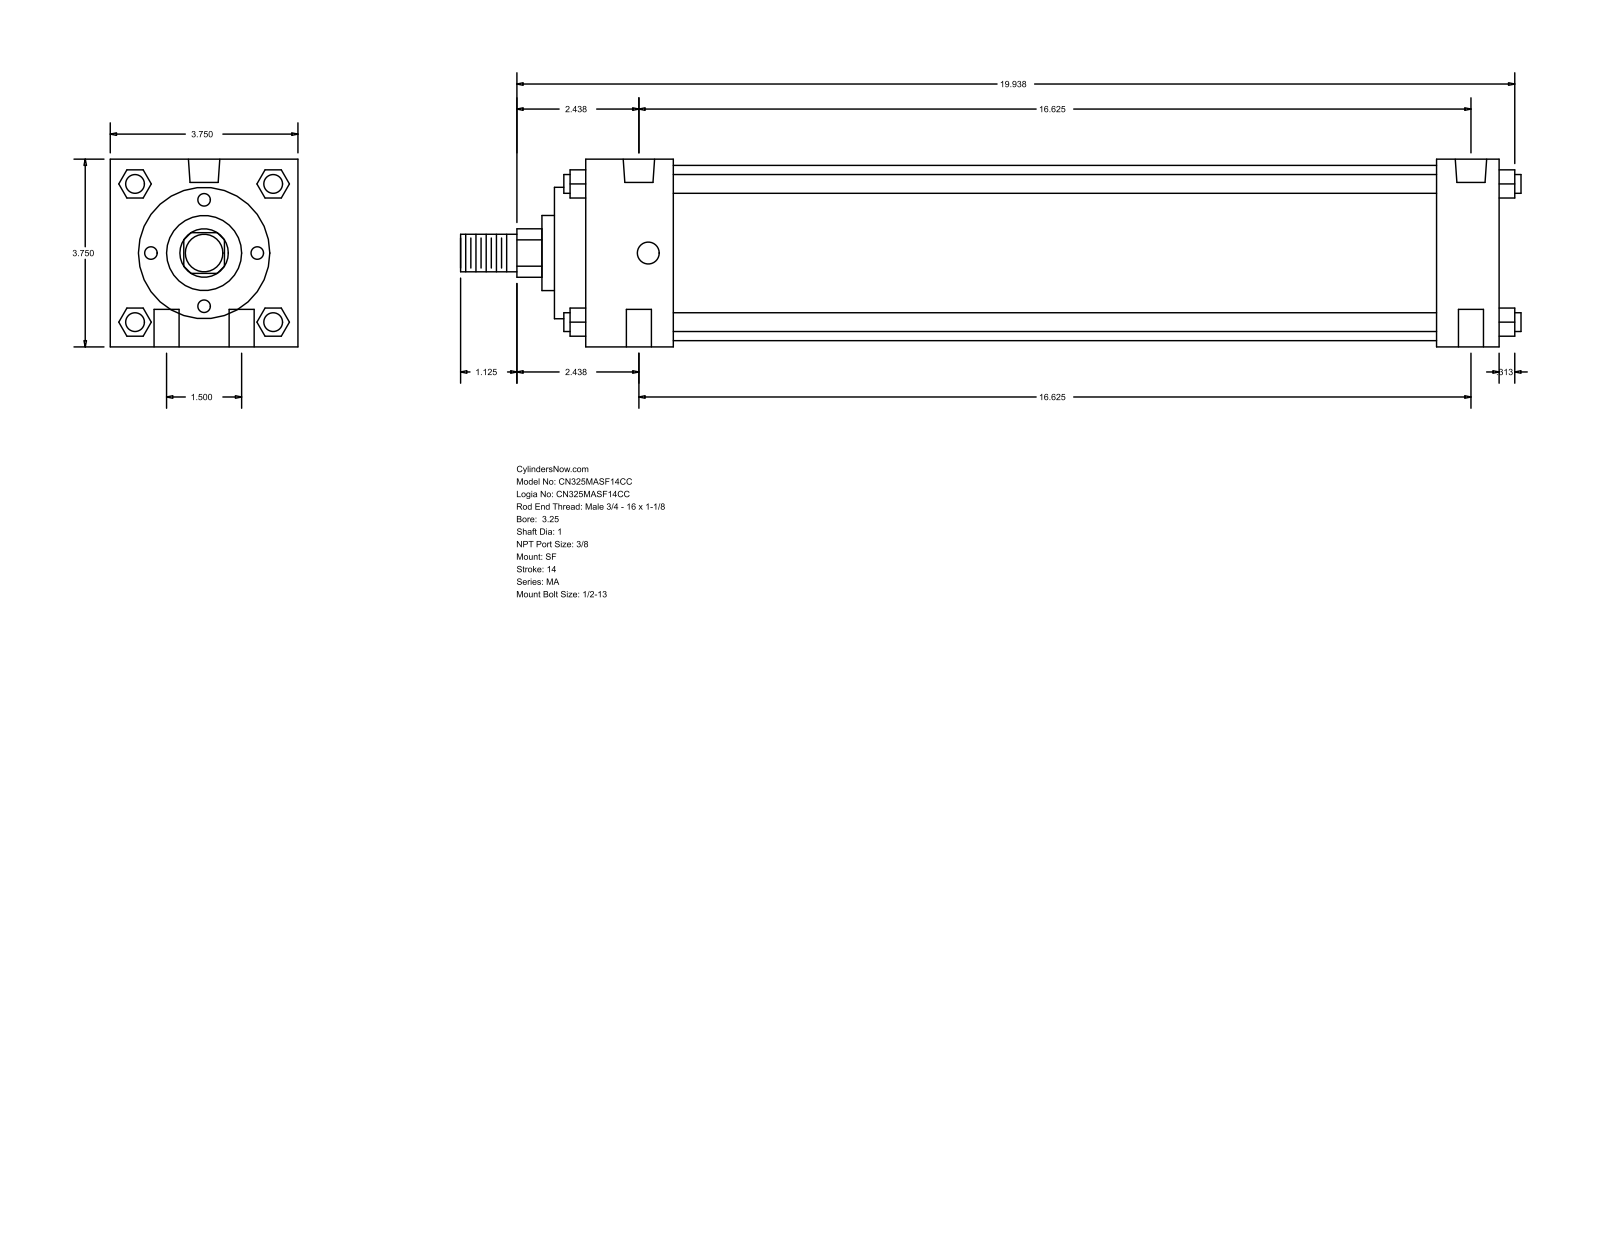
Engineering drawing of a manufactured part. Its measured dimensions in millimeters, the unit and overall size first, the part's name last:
Units: millimetres
Overall size (bounding box): 538.16 × 95.25 × 95.25
Round holes (diameter × count): ⌀12.7 ×4, ⌀11.11 ×2, ⌀15.93 ×2
Round bosses / shafts (diameter × count): ⌀9.53 ×4, ⌀88.9 ×1, ⌀66.67 ×1, ⌀38.1 ×1, ⌀25.4 ×1, ⌀19.05 ×1
Partial cylindrical surfaces — rounded edges, fillets, slot ends (radius × count): R12.29 ×1
Main face-to-face distances: 95.24, 463.56, 431.81, 31.75, 44.46, 387.35, 419.1, 15.87, 60.33, 447.68
Hole centre spacings: 19.05, 422.71, 422.28, 38.1, 424, 412.76
Bodies: 0 solids, 126 faces (95 planar, 31 cylindrical, 0 other)
Part name (STEP PRODUCT): MA_SF__0325_1
STEP written by: GSSL Pune (CONFIG_CONTROL_DESIGN)
